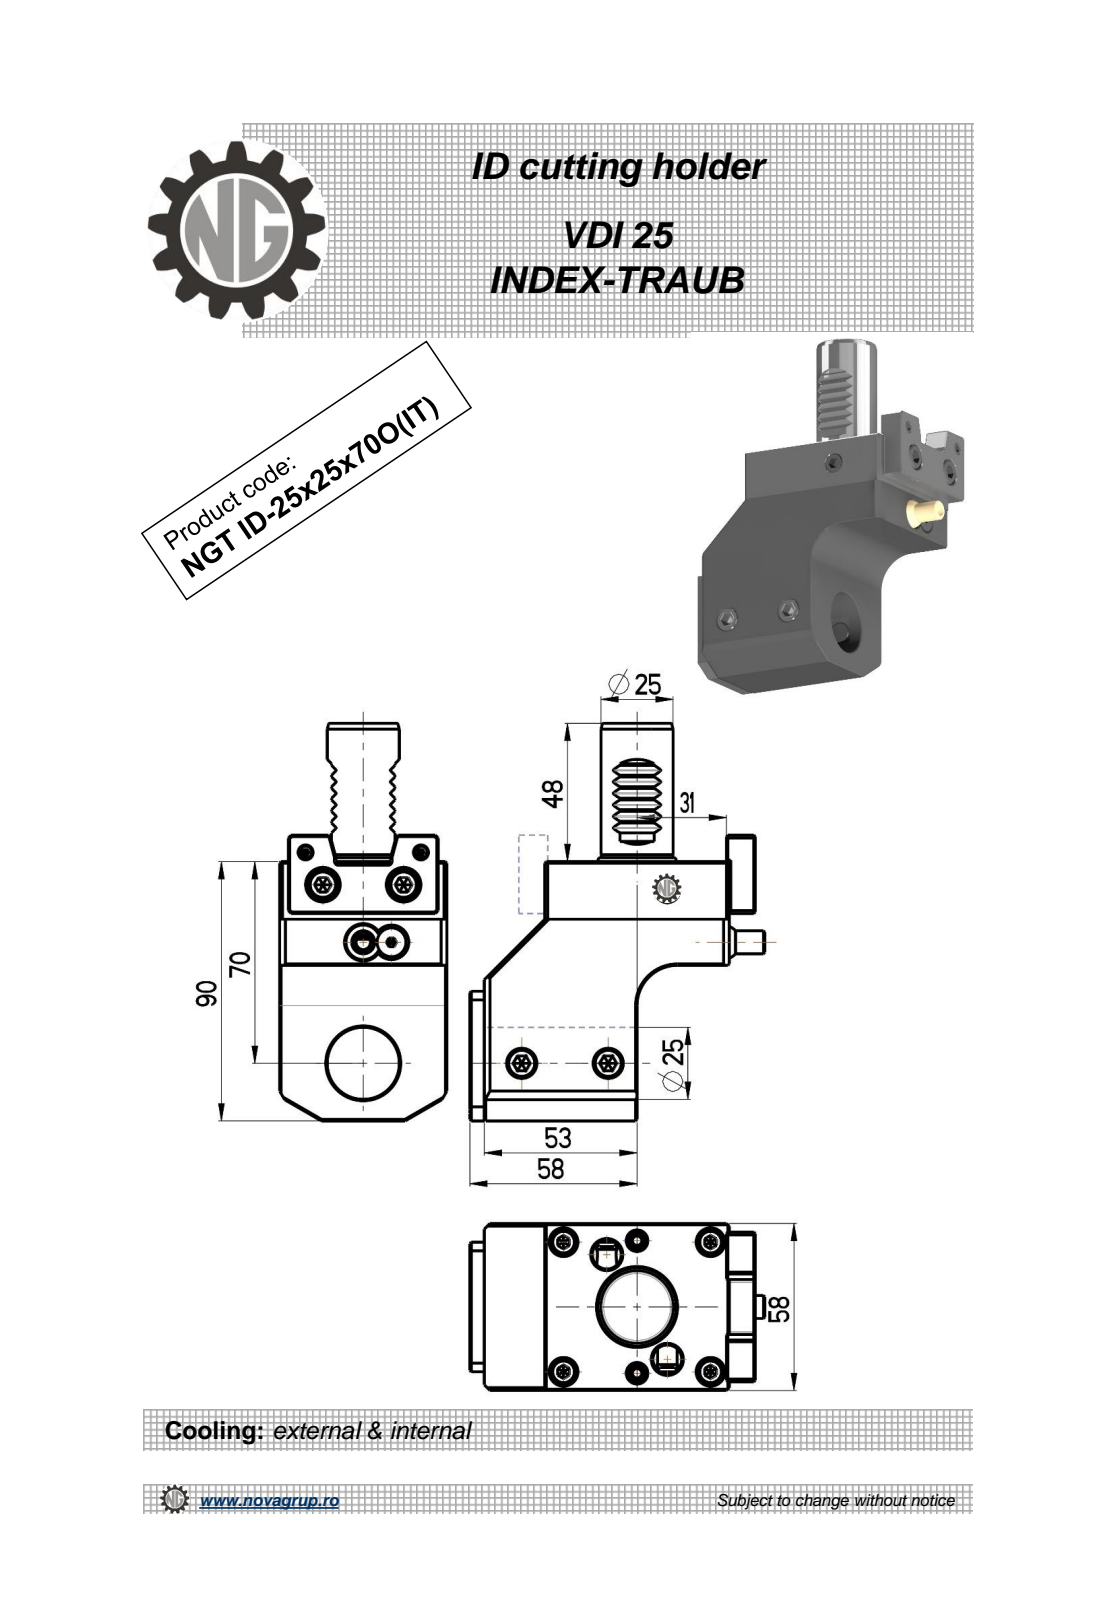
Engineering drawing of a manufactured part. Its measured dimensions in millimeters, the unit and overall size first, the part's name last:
Units: millimetres
Overall size (bounding box): 138 × 102.34 × 58
Round holes (diameter × count): ⌀5 ×3, ⌀4.2 ×2, ⌀10 ×2, ⌀25 ×1
Round bosses / shafts (diameter × count): ⌀10 ×4, ⌀25 ×1, ⌀8 ×1
Partial cylindrical surfaces — rounded edges, fillets, slot ends (radius × count): R0.2 ×20, R0.51 ×20, R0.3 ×12, R0.26 ×10, R1 ×2, R4.25 ×2, R8 ×2, R14 ×1
Main face-to-face distances: 58, 90, 32, 26, 41, 99, 9, 94, 53, 5
Hole centre spacings: 12.71, 24.41, 35.8, 37.06, 63.56, 75.88, 28, 40
Volume: 316 275 mm³ · Surface area: 42 172 mm²
Bodies: 1 solid, 493 faces (254 planar, 115 cylindrical, 124 other)
Part name (STEP PRODUCT): NGT_ID_25_25_70O_IT
STEP written by: PRO/ENGINEER BY PARAMETRIC TECHNOLOGY CORPORATION, 2010280 (CONFIG_CONTROL_DESIGN)
